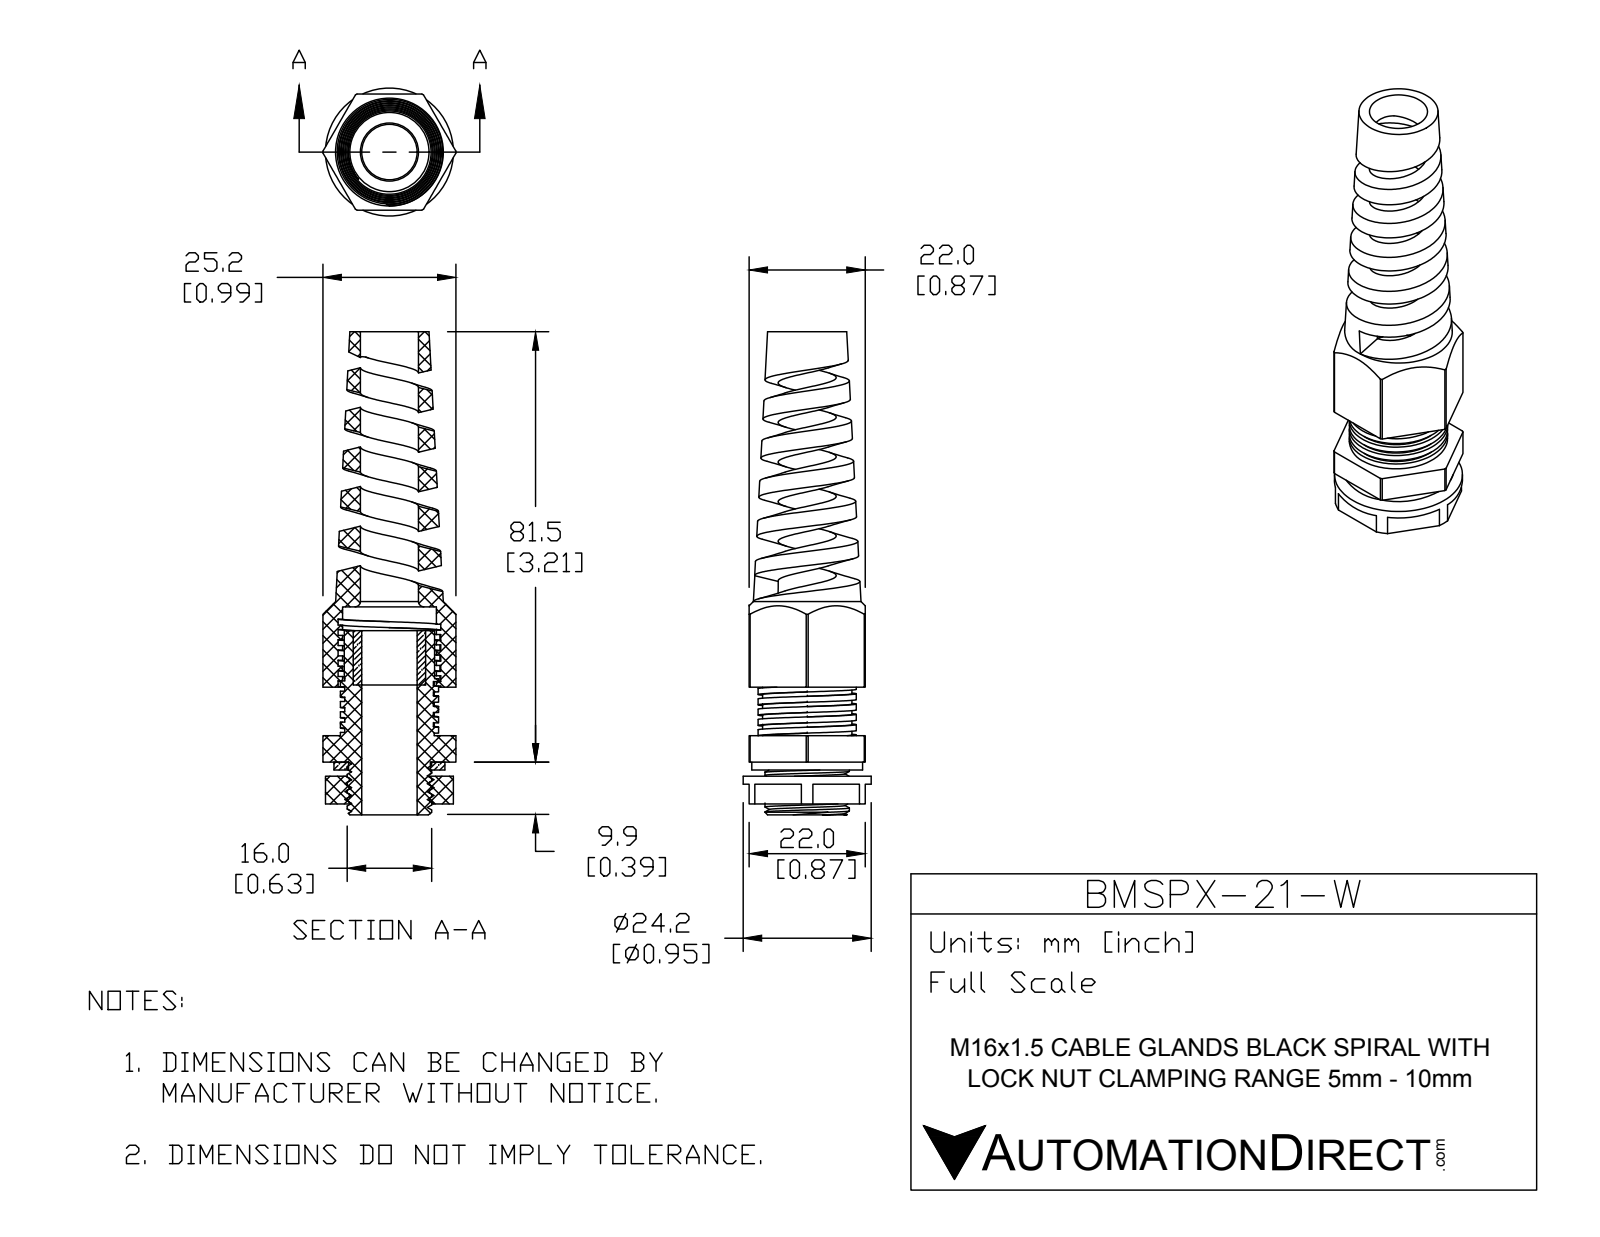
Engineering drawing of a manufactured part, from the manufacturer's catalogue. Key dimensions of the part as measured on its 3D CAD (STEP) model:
Part name (STEP PRODUCT): BMSPX-21-W
STEP written by: SolidWorks 2015 (CONFIG_CONTROL_DESIGN)
Units: millimetres
Bodies: 5 solids, 231 faces (103 planar, 93 cylindrical, 35 other)
Overall size (bounding box): 91.5 × 25.2 × 24.24
Volume: 14 083 mm³ · Surface area: 15 430 mm²
Round holes (diameter × count): ⌀10.5 ×1, ⌀11 ×1, ⌀13.7 ×1, ⌀15.18 ×1, ⌀15.5 ×1, ⌀17.78 ×1
Round bosses / shafts (diameter × count): ⌀24.24 ×1, ⌀21 ×1, ⌀18.61 ×1, ⌀17.1 ×1, ⌀16 ×1
Partial cylindrical surfaces — rounded edges, fillets, slot ends (radius × count): R12.6 ×1
Main face-to-face distances: 22, 2.5, 7.5, 5.25, 7.75, 1.5, 12.75, 5, 6.25, 1
